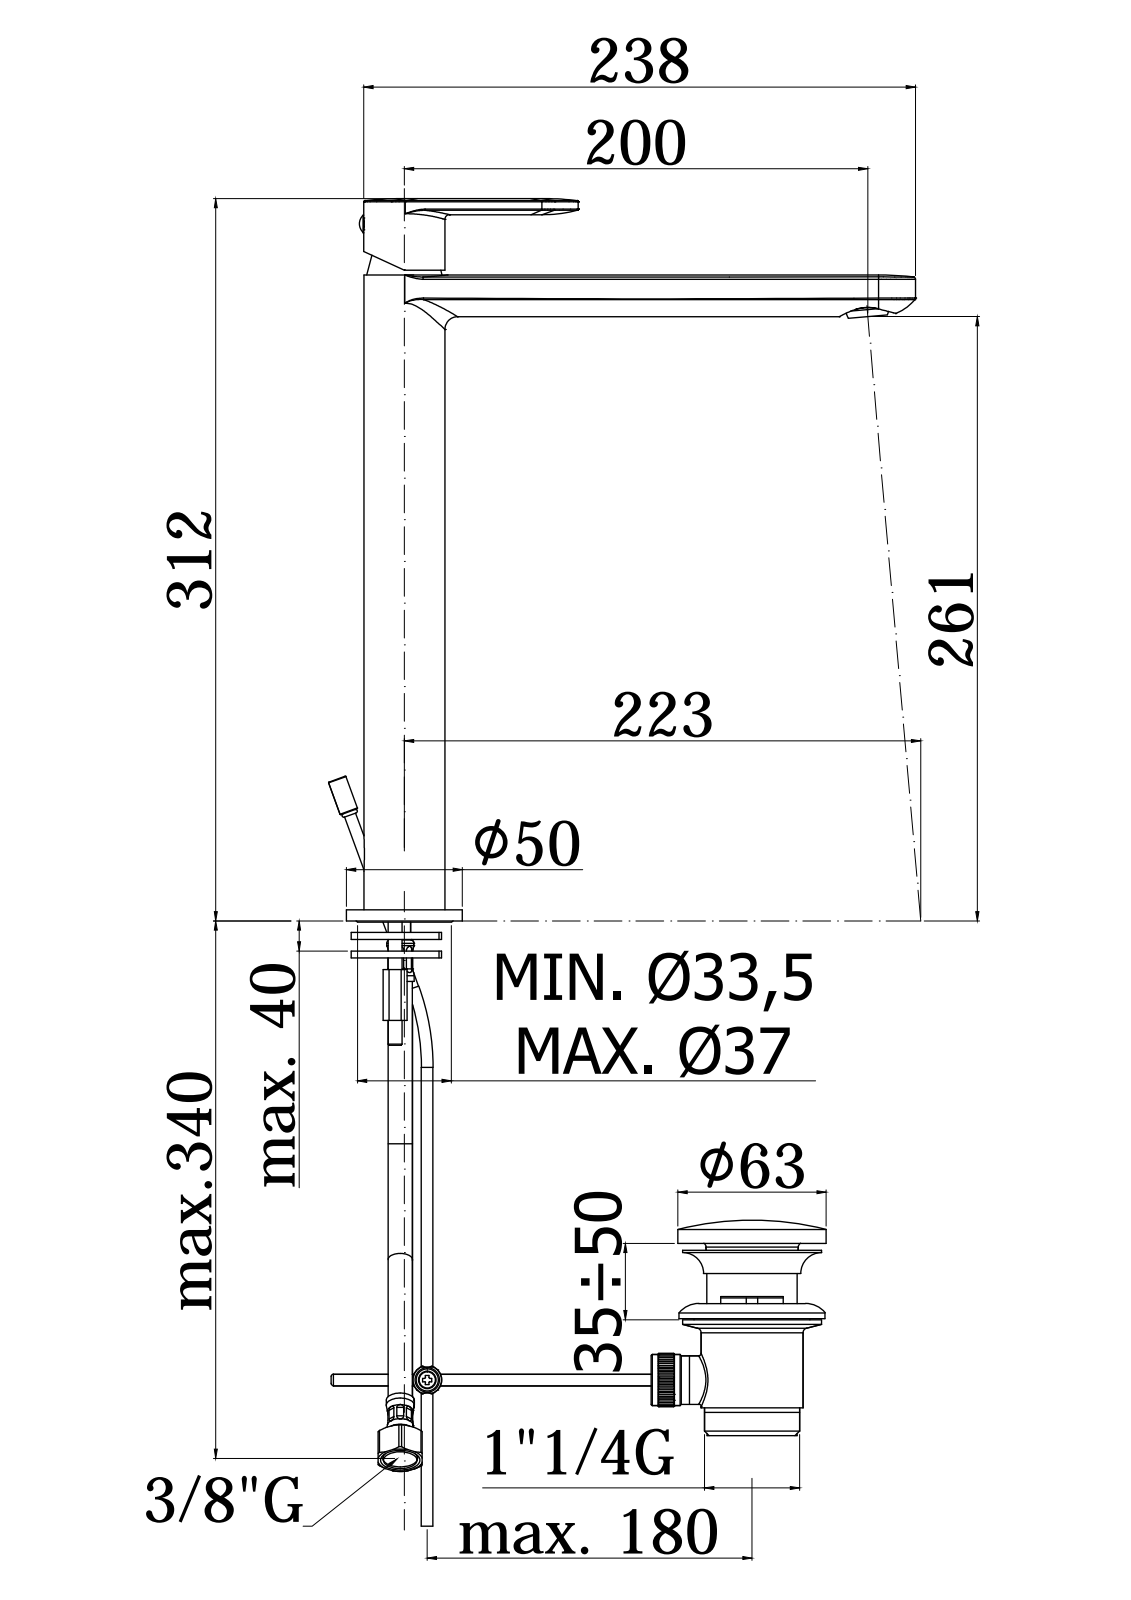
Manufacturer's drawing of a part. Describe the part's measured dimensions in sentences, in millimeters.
The part is named "CA085CR". Its 3-D file was written by "CREO PARAMETRIC BY PTC INC, 2020044 (CONFIG_CONTROL_DESIGN)". It is 3 solids with 192 faces: 63 planar, 62 cylindrical and 67 other. Overall it measures 310.32 by 255.73 by 50 millimeters. Its volume is 421 994 cubic millimeters and its surface area 70 264 square millimeters. Round holes: 1 of diameter 3, 1 of diameter 4.5, 1 of diameter 24.5, 1 of diameter 24.8, 1 of diameter 26.2, 1 of diameter 28. Round bosses or shafts: 1 of diameter 50, 1 of diameter 36, 1 of diameter 35, 1 of diameter 24, 1 of diameter 18.5, 1 of diameter 8, 1 of diameter 7.6, 1 of diameter 5.5. Partial cylindrical surfaces (rounded edges, fillets, slot ends): 4 of radius 3, 1 of radius 3.5, 1 of radius 9.75, 1 of radius 11.5, 1 of radius 16, 1 of radius 16.5, 1 of radius 27.5. The main face-to-face distances are 277.7, 4, 273.7, 307.32, 303.32, 29.62, 11.5, 2.5, 14, 9.
